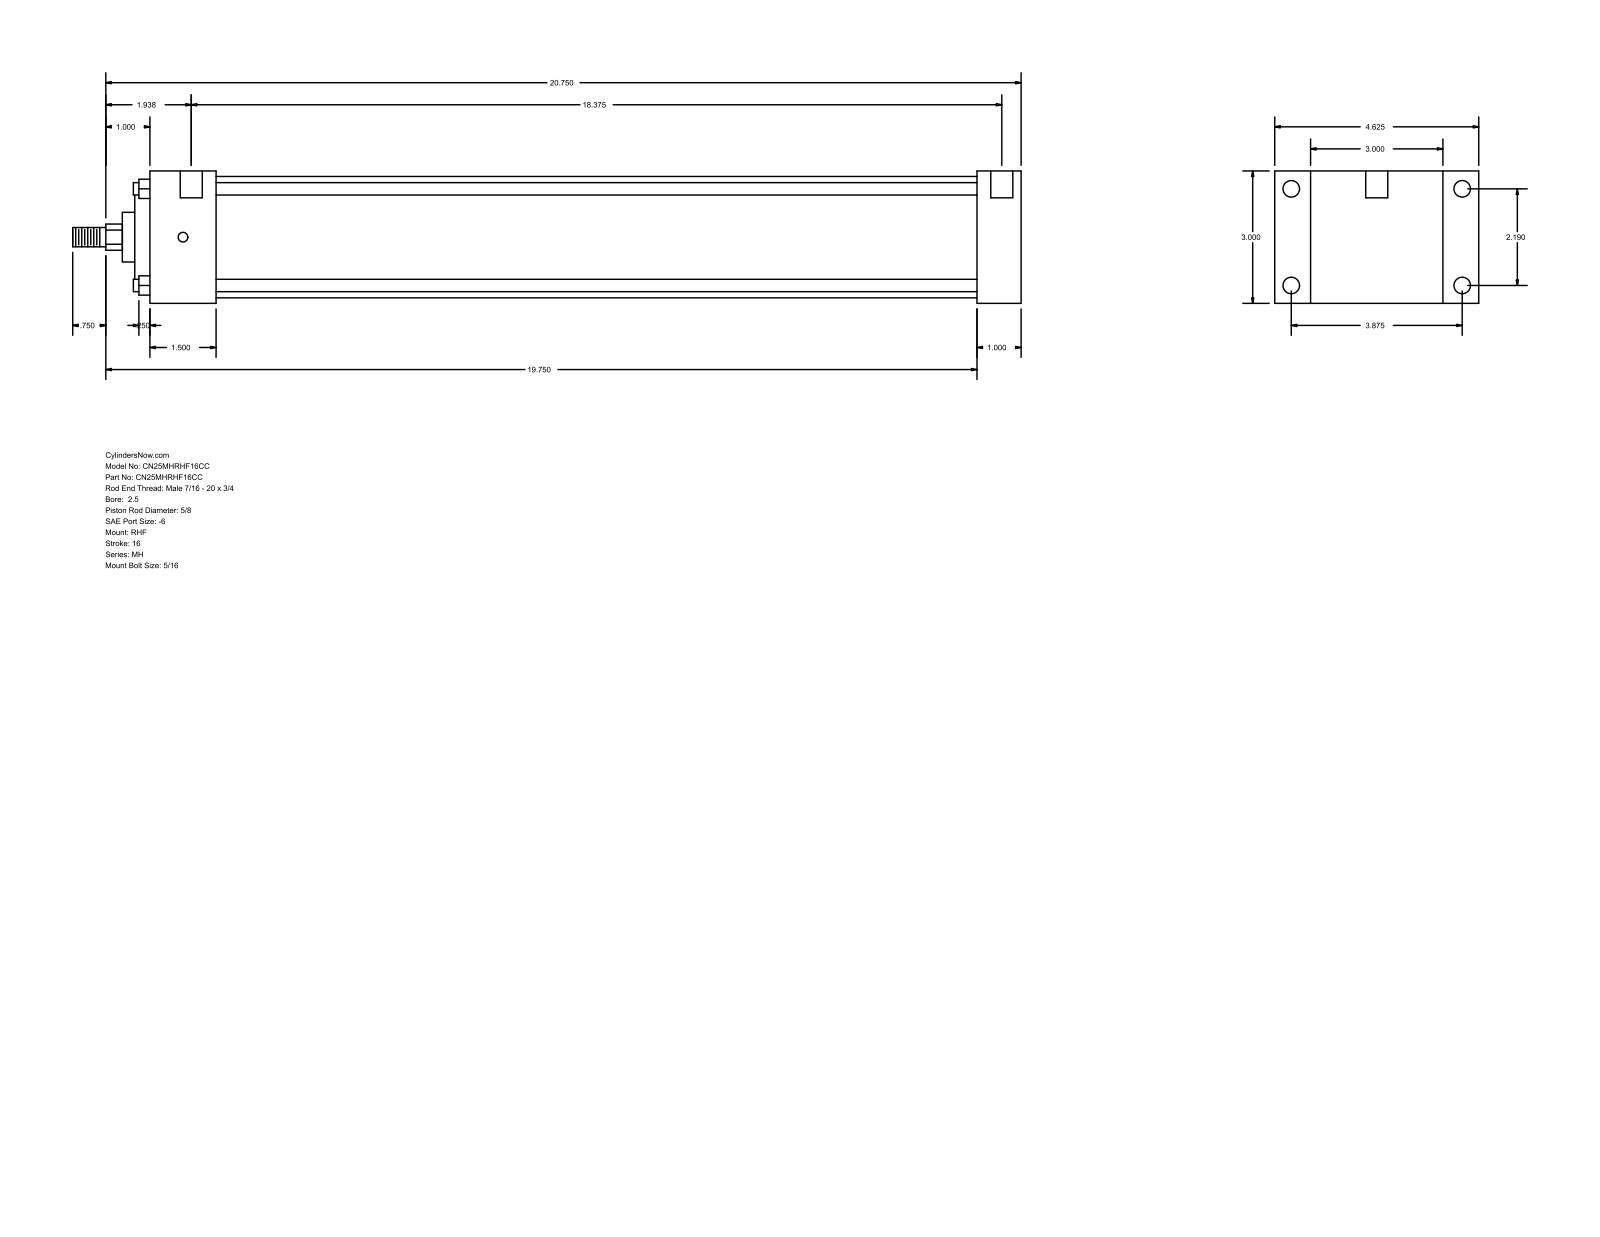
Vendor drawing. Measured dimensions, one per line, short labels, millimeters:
name: MH_RHF__0250_0.625
written by: GSSL Pune (CONFIG_CONTROL_DESIGN)
unit: mm
bodies: 0 solids, 90 faces (61 planar, 29 cylindrical, 0 other)
size: 546.1 × 117.47 × 76.2
holes: 4× ⌀5.56, 4× ⌀9.53, 2× ⌀12.7
bosses: 4× ⌀7.14, 1× ⌀69.85, 1× ⌀55.55, 1× ⌀28.57, 1× ⌀15.88, 1× ⌀11.11
rounds: 1× R7.54
face distances: 76.2, 25.4, 20.64, 96.84, 501.65, 476.25, 38.1, 117.48, 438.15, 463.55
hole spacings: 55.62, 98.42, 113.05, 474.66, 3.17, 4.76, 466.73, 469.9
